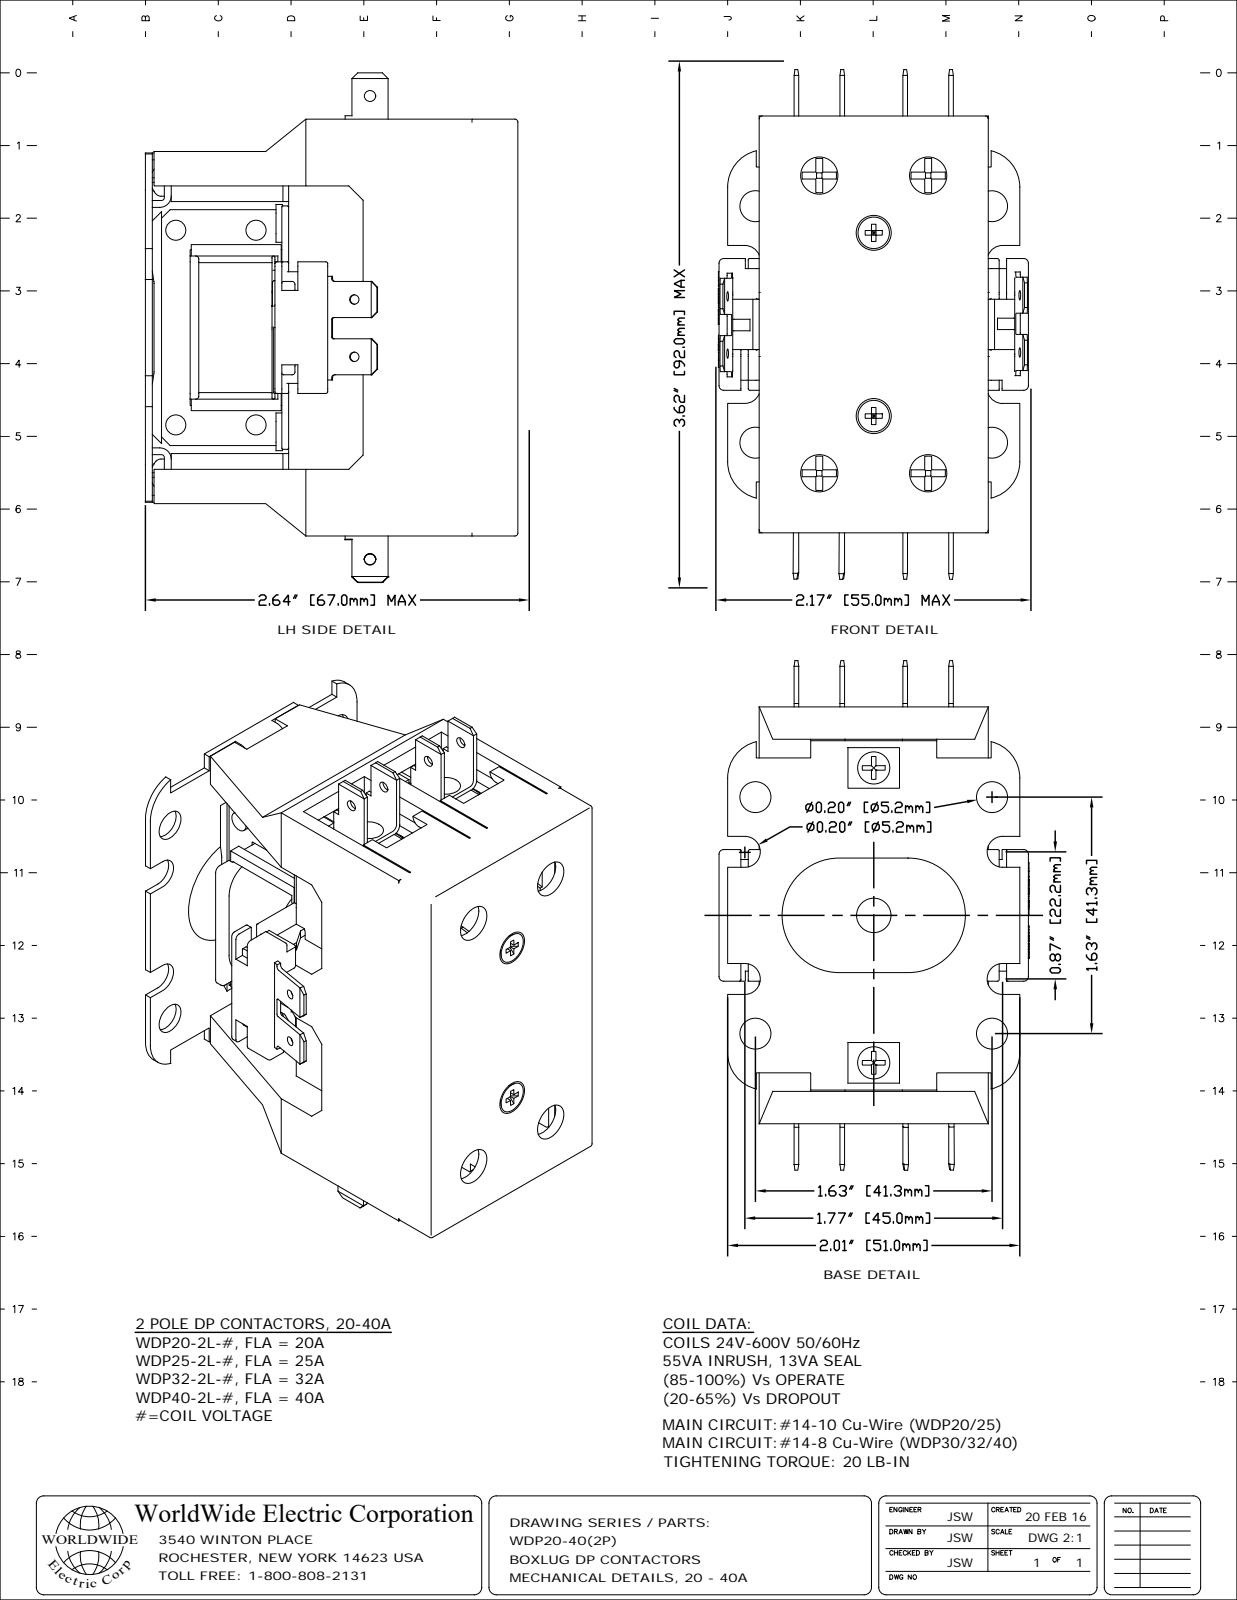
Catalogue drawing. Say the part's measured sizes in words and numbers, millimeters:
The part is named "WDP30-2L-230". Its 3-D file was written by "SolidWorks 2017 (AUTOMOTIVE_DESIGN)". It is 4 solids with 2745 faces: 1788 planar, 642 cylindrical and 315 other. Overall it measures 89 by 65 by 54.1 millimeters. Its volume is 95 720 cubic millimeters and its surface area 66 900 square millimeters. Round holes: 6 of diameter 3, 6 of diameter 3.1, 4 of diameter 1.7, 4 of diameter 2.5, 4 of diameter 4.5, 4 of diameter 5.4, 4 of diameter 6.5, 2 of diameter 2, 2 of diameter 2.6, 1 of diameter 6. Round bosses or shafts: 9 of diameter 3.5, 4 of diameter 6, 4 of diameter 5, 4 of diameter 3.8, 2 of diameter 6.5, 2 of diameter 5.6, 2 of diameter 4.8, 2 of diameter 4.2. Partial cylindrical surfaces (rounded edges, fillets, slot ends): 88 of radius 0.5, 82 of radius 0.2, 68 of radius 0.3, 34 of radius 1, 30 of radius 1.5, 12 of radius 2, 8 of radius 1.2, 6 of radius 0.8. The main face-to-face distances are 40, 1.2, 1.5, 19, 2, 9.5, 38.5, 6.7, 23.8, 37. The hole center spacings are 19, 32.2, 8, 8.5, 9.5, 9.5, 9.6, 11.5.
